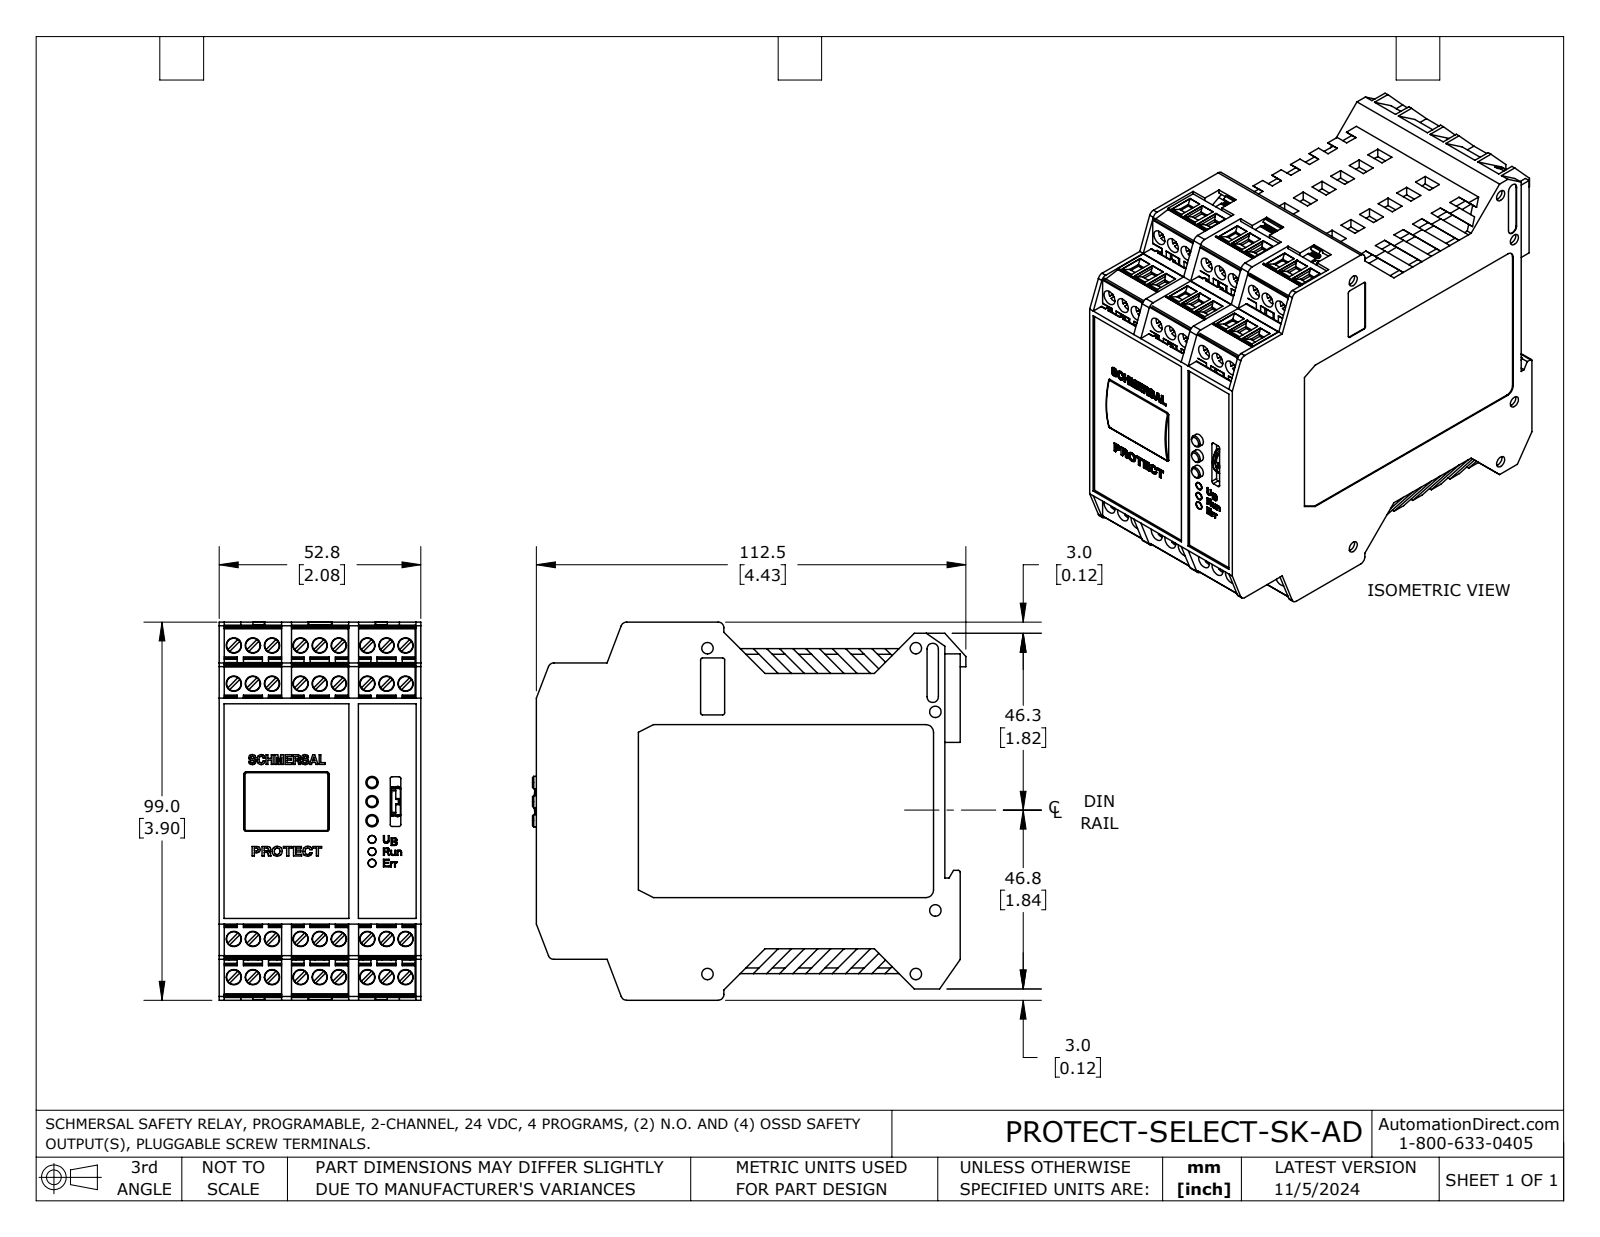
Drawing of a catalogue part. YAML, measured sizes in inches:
part_name: "PROTECT-SELECT-SK-AD_REV2"
step_written_by: "SolidWorks 2023 (AUTOMOTIVE_DESIGN)"
units: inches
bodies: {solids: 13, faces: 3525, planar: 2823, cylindrical: 535, other: 167}
overall_size: [4.469, 3.898, 2.079]
volume: 29.72
surface_area: 118.1
round_holes:
  - {diameter: 0.157, count: 36}
  - {diameter: 0.055, count: 18}
  - {diameter: 0.11, count: 18}
  - {diameter: 0.118, count: 6}
  - {diameter: 0.079, count: 5}
round_bosses_or_shafts:
  - {diameter: 0.149, count: 36}
  - {diameter: 0.126, count: 3}
  - {diameter: 0.083, count: 3}
partial_cylinders:
  - {radius: 0.02, count: 27}
  - {radius: 0.008, count: 19}
  - {radius: 0.115, count: 18}
  - {radius: 0.012, count: 16}
  - {radius: 0.059, count: 10}
  - {radius: 0.016, count: 4}
  - {radius: 0.03, count: 4}
  - {radius: 0.031, count: 3}
face_to_face_distances: [2.071, 0.591, 2.079, 1.437, 0.728, 0.693, 0.051, 0.642, 2.063, 2.02]
hole_center_spacings: [0.197, 0.689, 0.394, 0.492, 0.886, 0.794, 3.103, 0.44]
